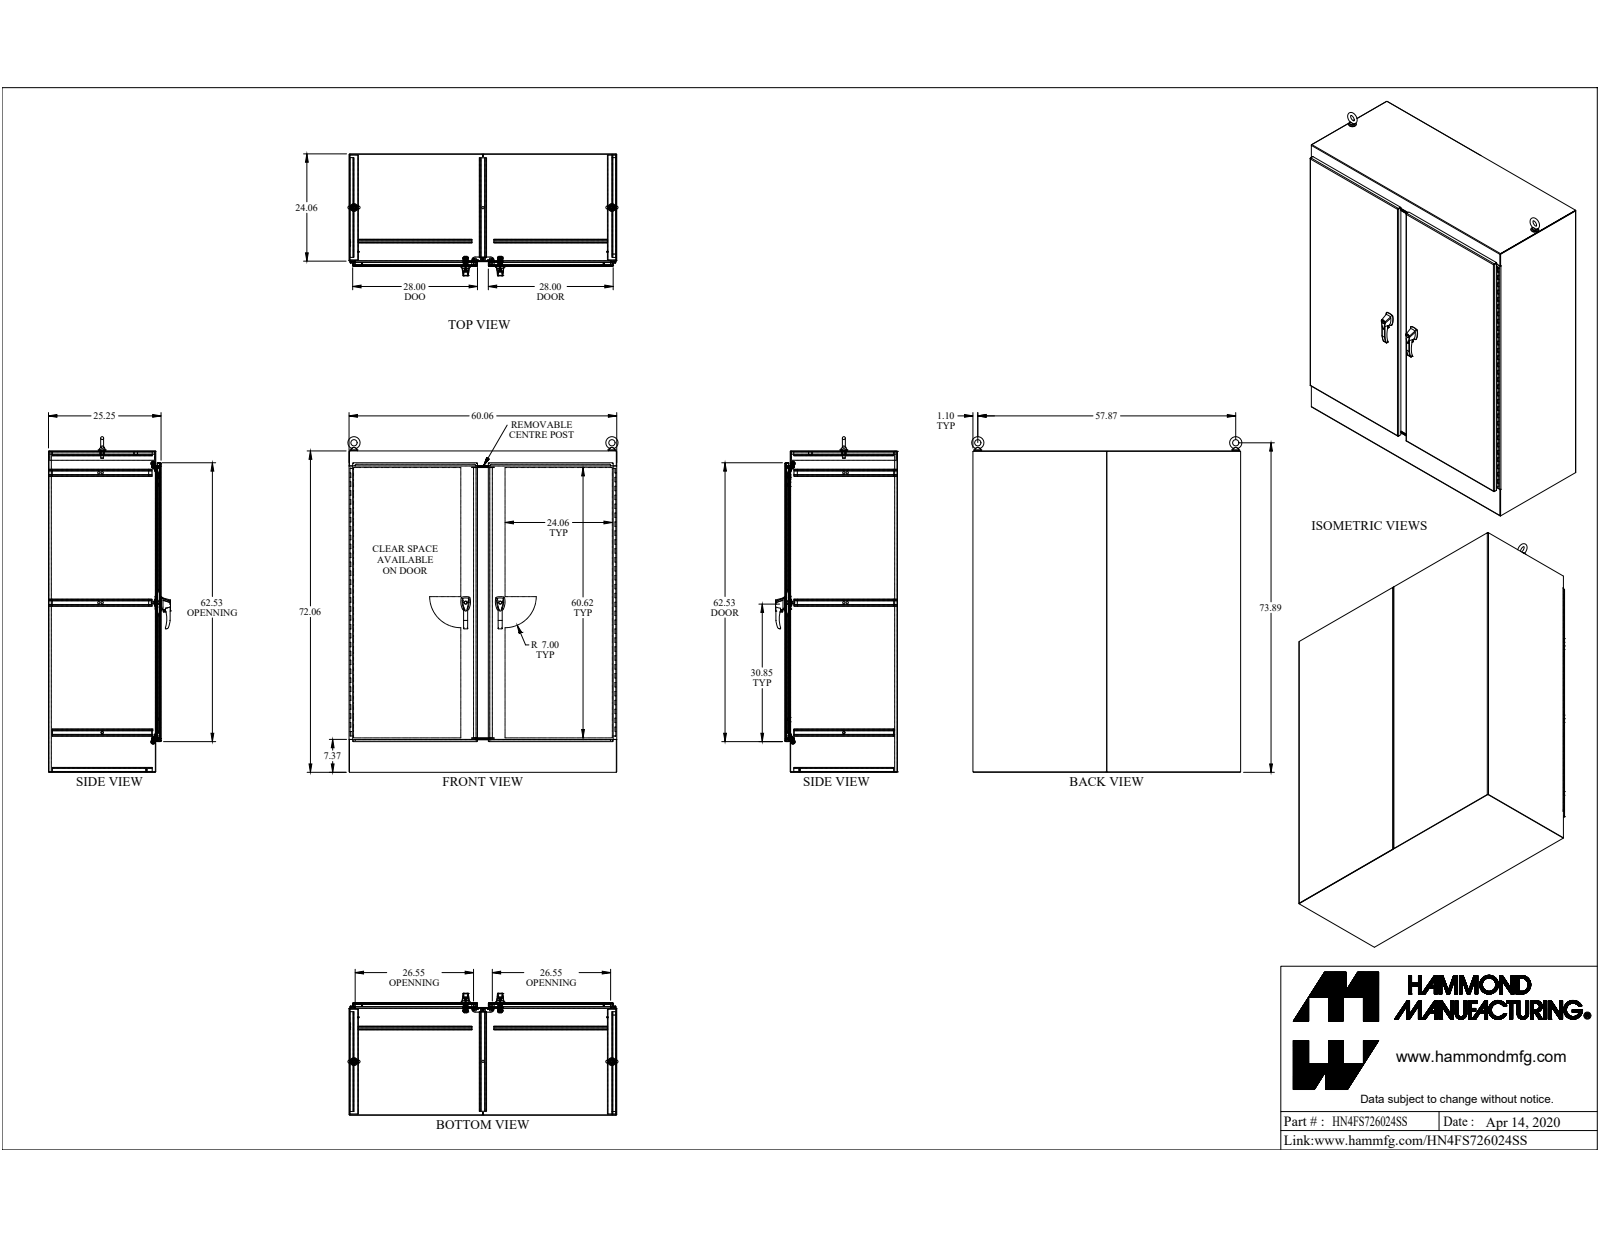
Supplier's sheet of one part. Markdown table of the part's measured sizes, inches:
| quantity | value |
| --- | --- |
| part name | HN4FS726024SS |
| STEP written by | SolidWorks 2019 (CONFIG_CONTROL_DESIGN) |
| units | inches |
| bodies | 106 solids, 2965 faces (1563 planar, 1156 cylindrical, 246 other) |
| overall size | 75.256 × 60.604 × 27.362 |
| volume | 1 738 in³ |
| surface area | 36 672 in² |
| round holes (diameter × count) | 0.304 × 20, 0.35 × 8, 0.25 × 7, 0.5 × 7, 0.257 × 4, 0.28 × 4, 0.281 × 4, 0.313 × 4, 0.39 × 4, 0.413 × 4, 0.201 × 3, 0.313 × 3 |
| round bosses / shafts (diameter × count) | 1 × 4, 0.75 × 4, 0.63 × 4, 0.625 × 4, 0.44 × 4, 0.37 × 4, 0.313 × 4, 0.25 × 4 |
| partial cylindrical surfaces (radius × count) | 0.043 × 54, 0.138 × 48, 0.5 × 33, 0.1 × 28, 0.125 × 27, 0.018 × 24, 0.06 × 24, 0.318 × 18 |
| main face-to-face distances | 0.095, 25.152, 25.057, 25.247, 59.965, 71.965, 59.87, 1.187, 23.965, 60.06 |
| hole center spacings | 6, 58.636, 12, 59.55, 18, 61.043, 24, 63.073 |
